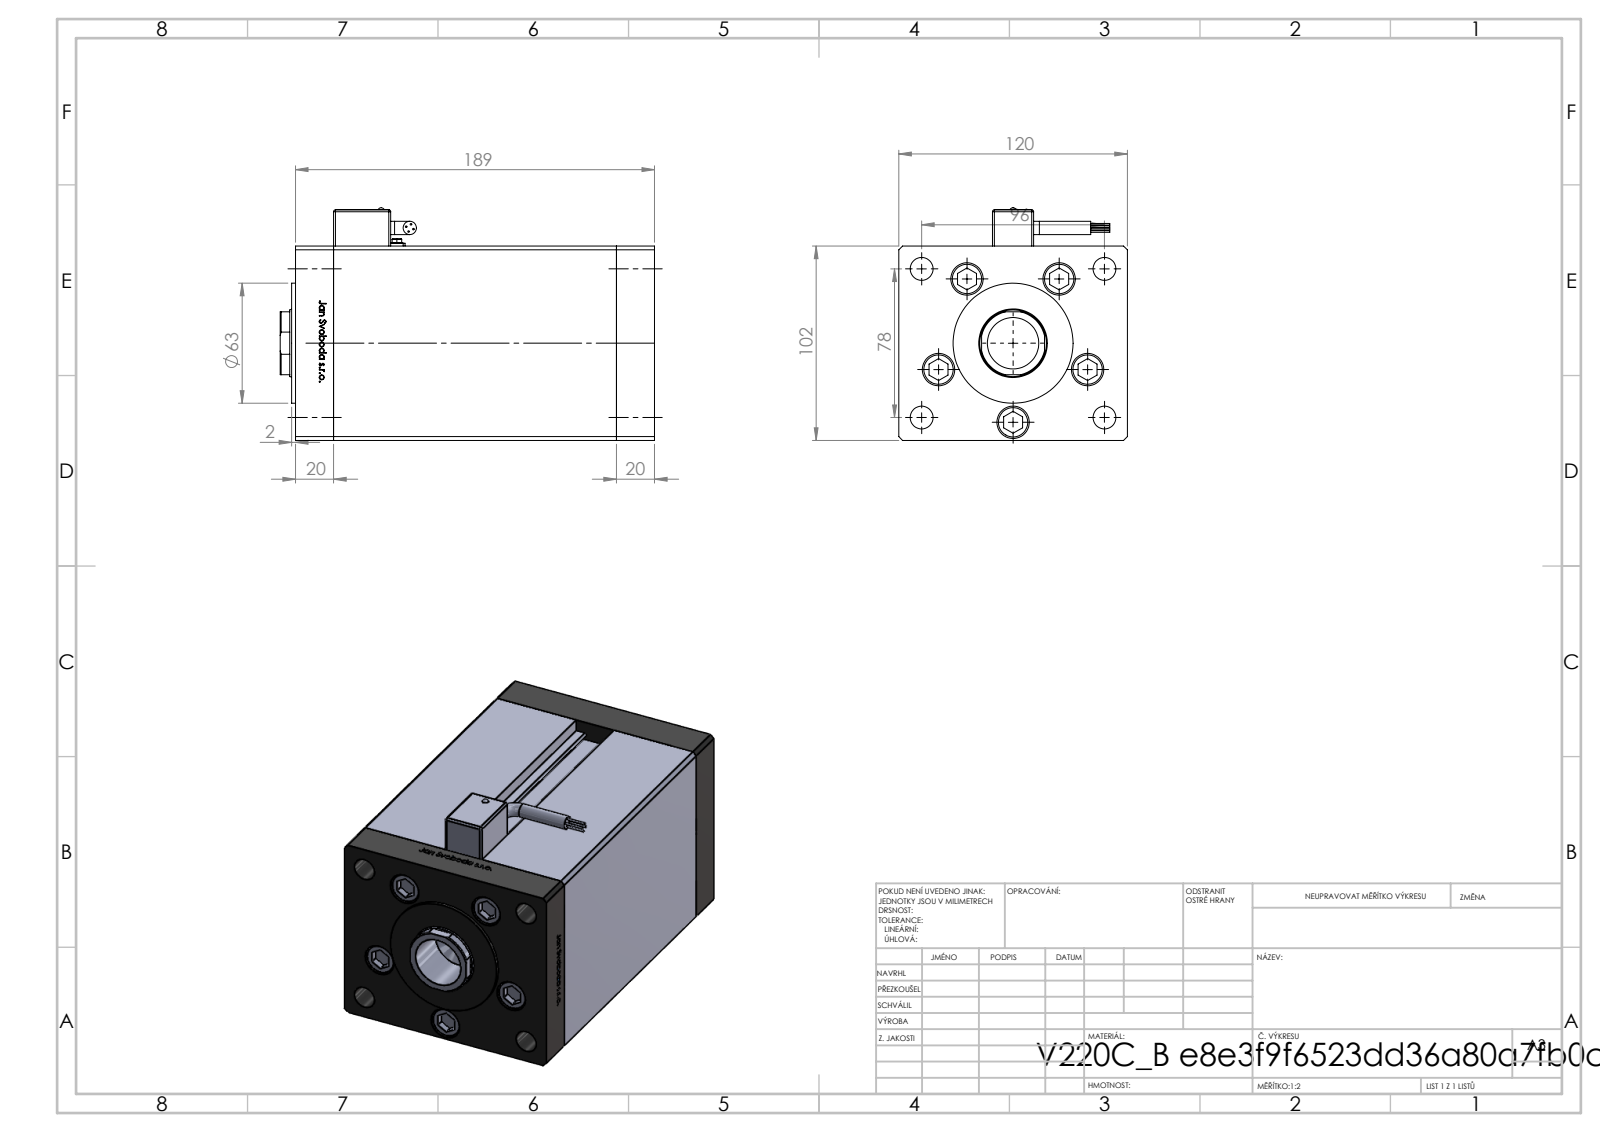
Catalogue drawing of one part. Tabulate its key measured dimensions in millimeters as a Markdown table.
| quantity | value |
| --- | --- |
| part name | ALLEN BOLT; V220C_B MIDDLE; V220C_B_VC; V220C_FRONT_B (+2 more) |
| STEP written by | SolidWorks 2019 (CONFIG_CONTROL_DESIGN) |
| units | millimeters |
| bodies | 15 solids, 1279 faces (501 planar, 188 cylindrical, 590 other) |
| overall size | 196.5 × 122.1 × 120 |
| volume | 2 071 000 mm³ |
| surface area | 254 633 mm² |
| round holes (diameter × count) | 13.5 × 5, 17 × 5, 12 × 4, 2 × 2, 13.16 × 2, 3.6 × 1, 5 × 1, 7 × 1, 27 × 1, 36 × 1 |
| round bosses / shafts (diameter × count) | 8 × 5, 0.85 × 4, 7 × 2, 63 × 1, 6 × 1, 3.5 × 1, 2.5 × 1 |
| partial cylindrical surfaces (radius × count) | 1 × 14, 0.93 × 2, 4 × 2, 17.5 × 1 |
| main face-to-face distances | 102, 148.5, 120, 20, 168.5, 188.5, 11, 170.5, 9, 4 |
| hole center spacings | 41.5, 61.85, 24.39, 26.69, 47.92, 48.07, 49.84, 53.57 |
